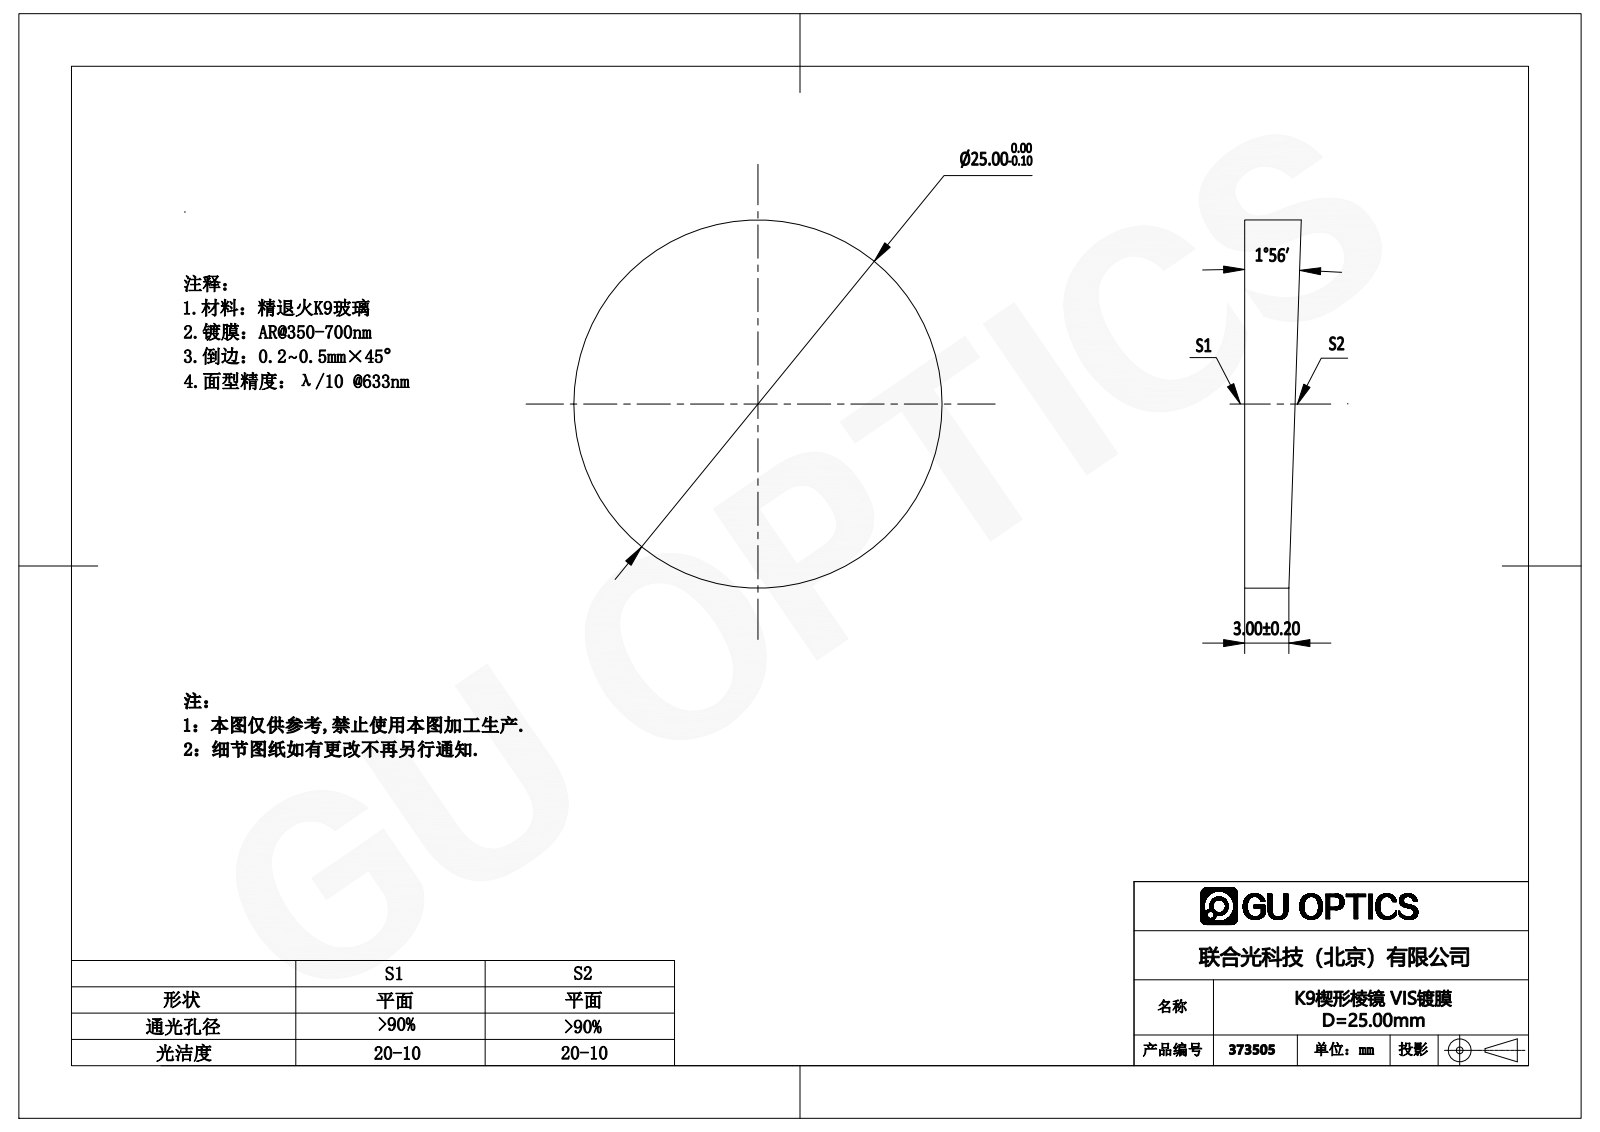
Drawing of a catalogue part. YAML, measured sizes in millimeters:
part_name: "373501"
step_written_by: "SolidWorks 2016 (CONFIG_CONTROL_DESIGN)"
units: millimeters
bodies: {solids: 1, faces: 4, planar: 2, cylindrical: 2, other: 0}
overall_size: [25, 25, 3.84]
volume: 1679
surface_area: 1251
round_bosses_or_shafts:
  - {diameter: 25, count: 1}
